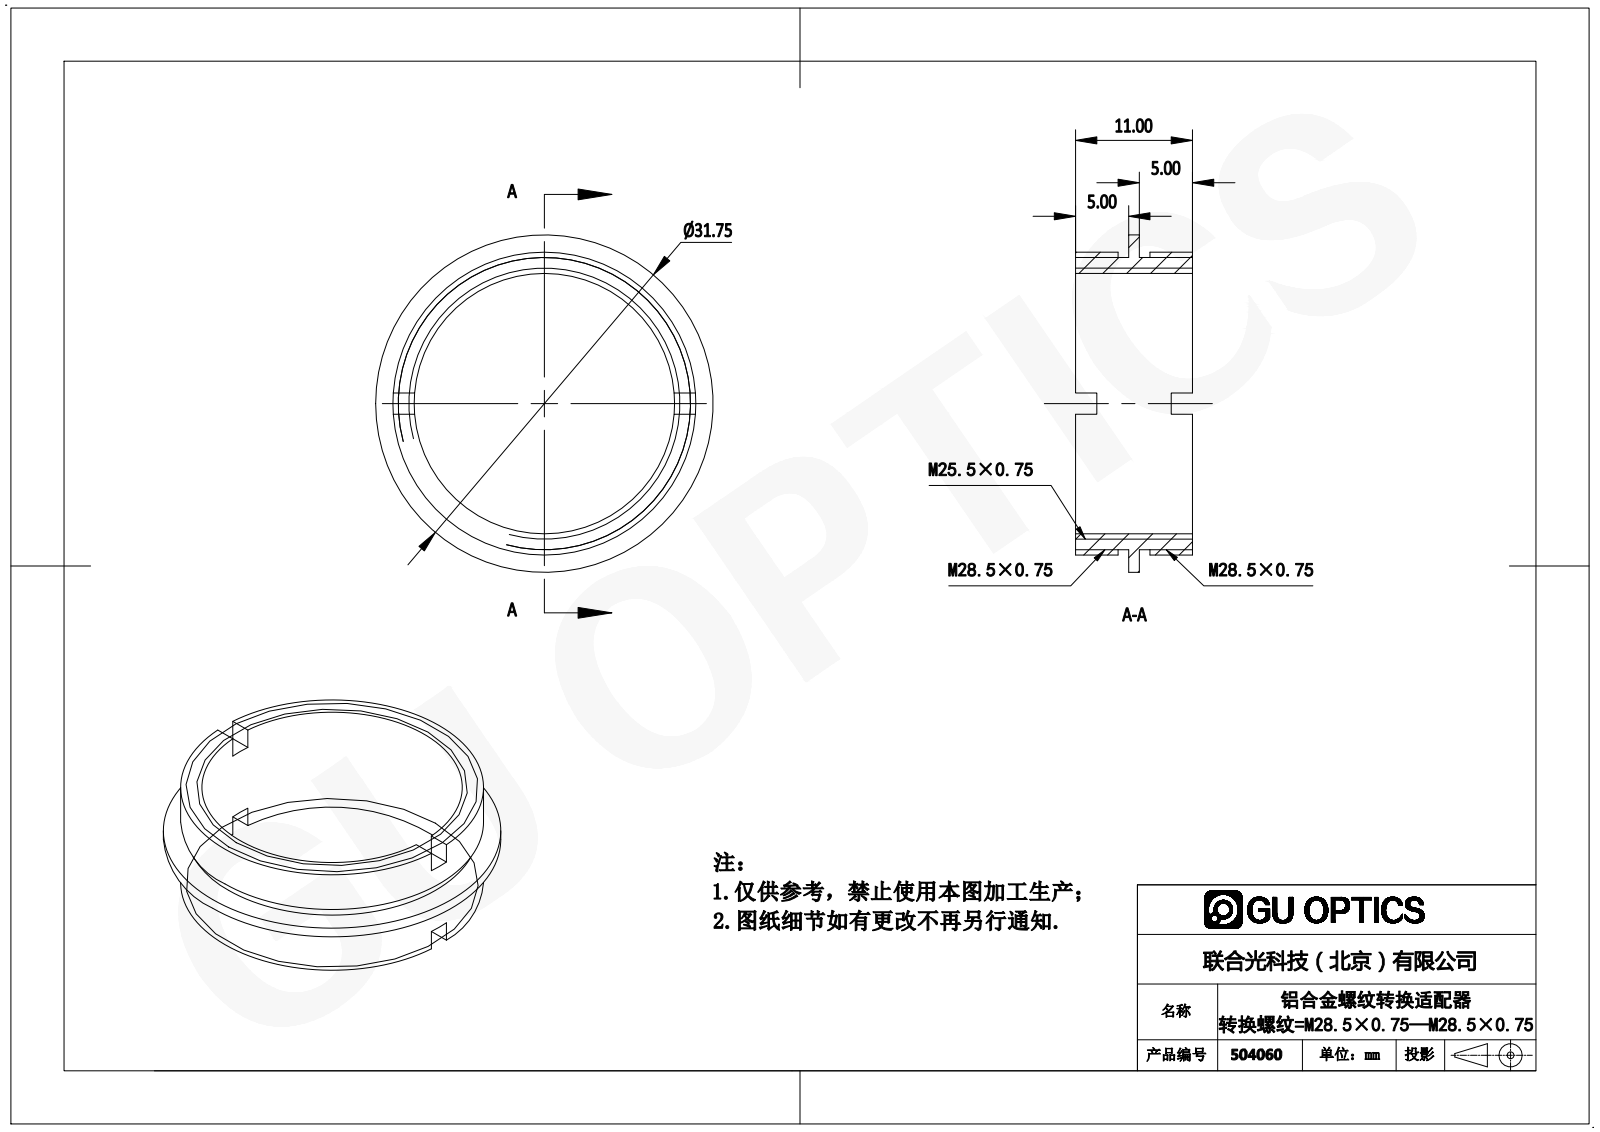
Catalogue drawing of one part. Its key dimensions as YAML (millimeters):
part_name: "504060"
step_written_by: "SolidWorks 2016 (AUTOMOTIVE_DESIGN)"
units: millimeters
bodies: {solids: 1, faces: 32, planar: 20, cylindrical: 12, other: 0}
overall_size: [31.75, 31.75, 11]
volume: 1865
surface_area: 2652
round_holes:
  - {diameter: 24.5, count: 1}
round_bosses_or_shafts:
  - {diameter: 31.75, count: 1}
  - {diameter: 28.5, count: 1}
  - {diameter: 27.5, count: 1}
face_to_face_distances: [5, 6, 1, 11, 2, 4, 7, 3, 9]
